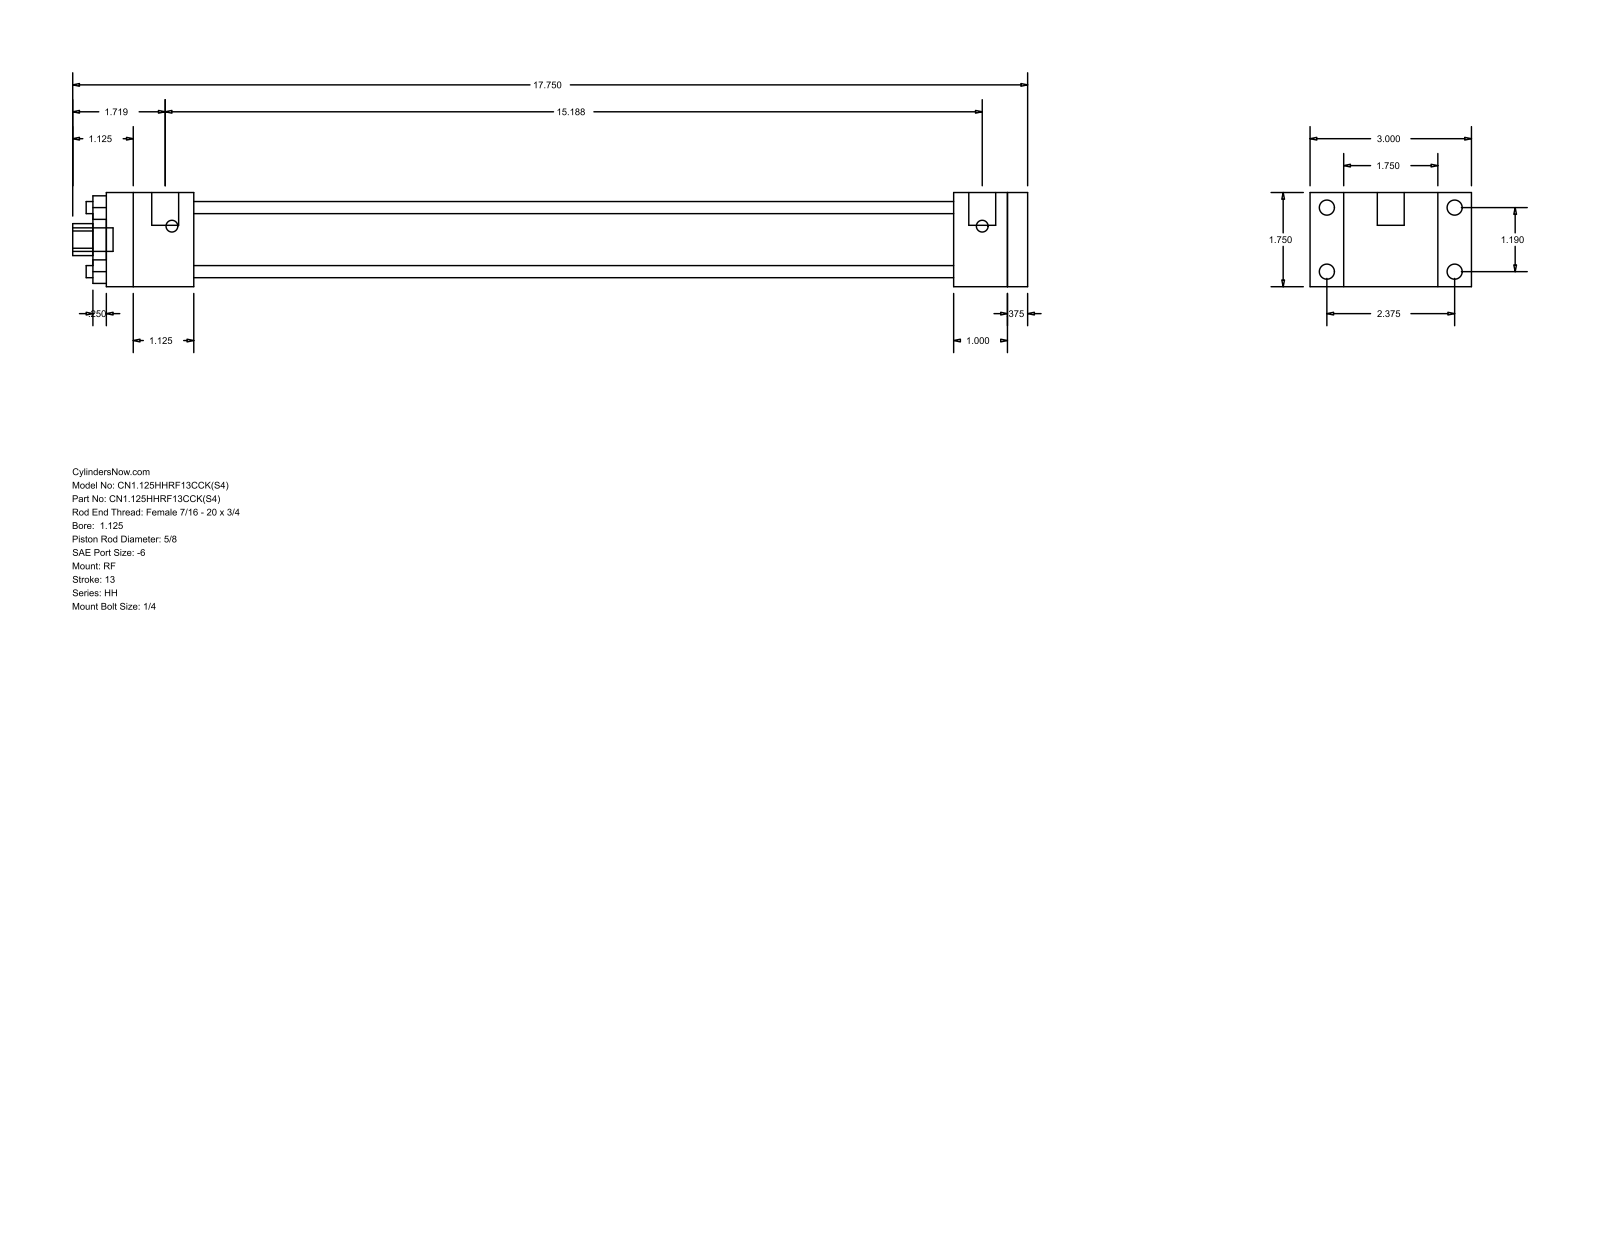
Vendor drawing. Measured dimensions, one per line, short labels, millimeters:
name: HH_RF__0112_0.625
written by: GSSL Pune (CONFIG_CONTROL_DESIGN)
unit: mm
bodies: 0 solids, 92 faces (64 planar, 28 cylindrical, 0 other)
size: 450.85 × 76.2 × 44.45
holes: 4× ⌀5.71, 1× ⌀15.88, 1× ⌀28.57, 1× ⌀34.92
bosses: 4× ⌀7.14, 4× ⌀5.56, 2× ⌀12.7, 1× ⌀11.11
rounds: 1× R7.54
face distances: 44.46, 9.53, 434.97, 15.87, 384.17, 393.7, 358.78, 25.39, 34.92, 41.27
hole spacings: 21.37, 30.22, 42.74
